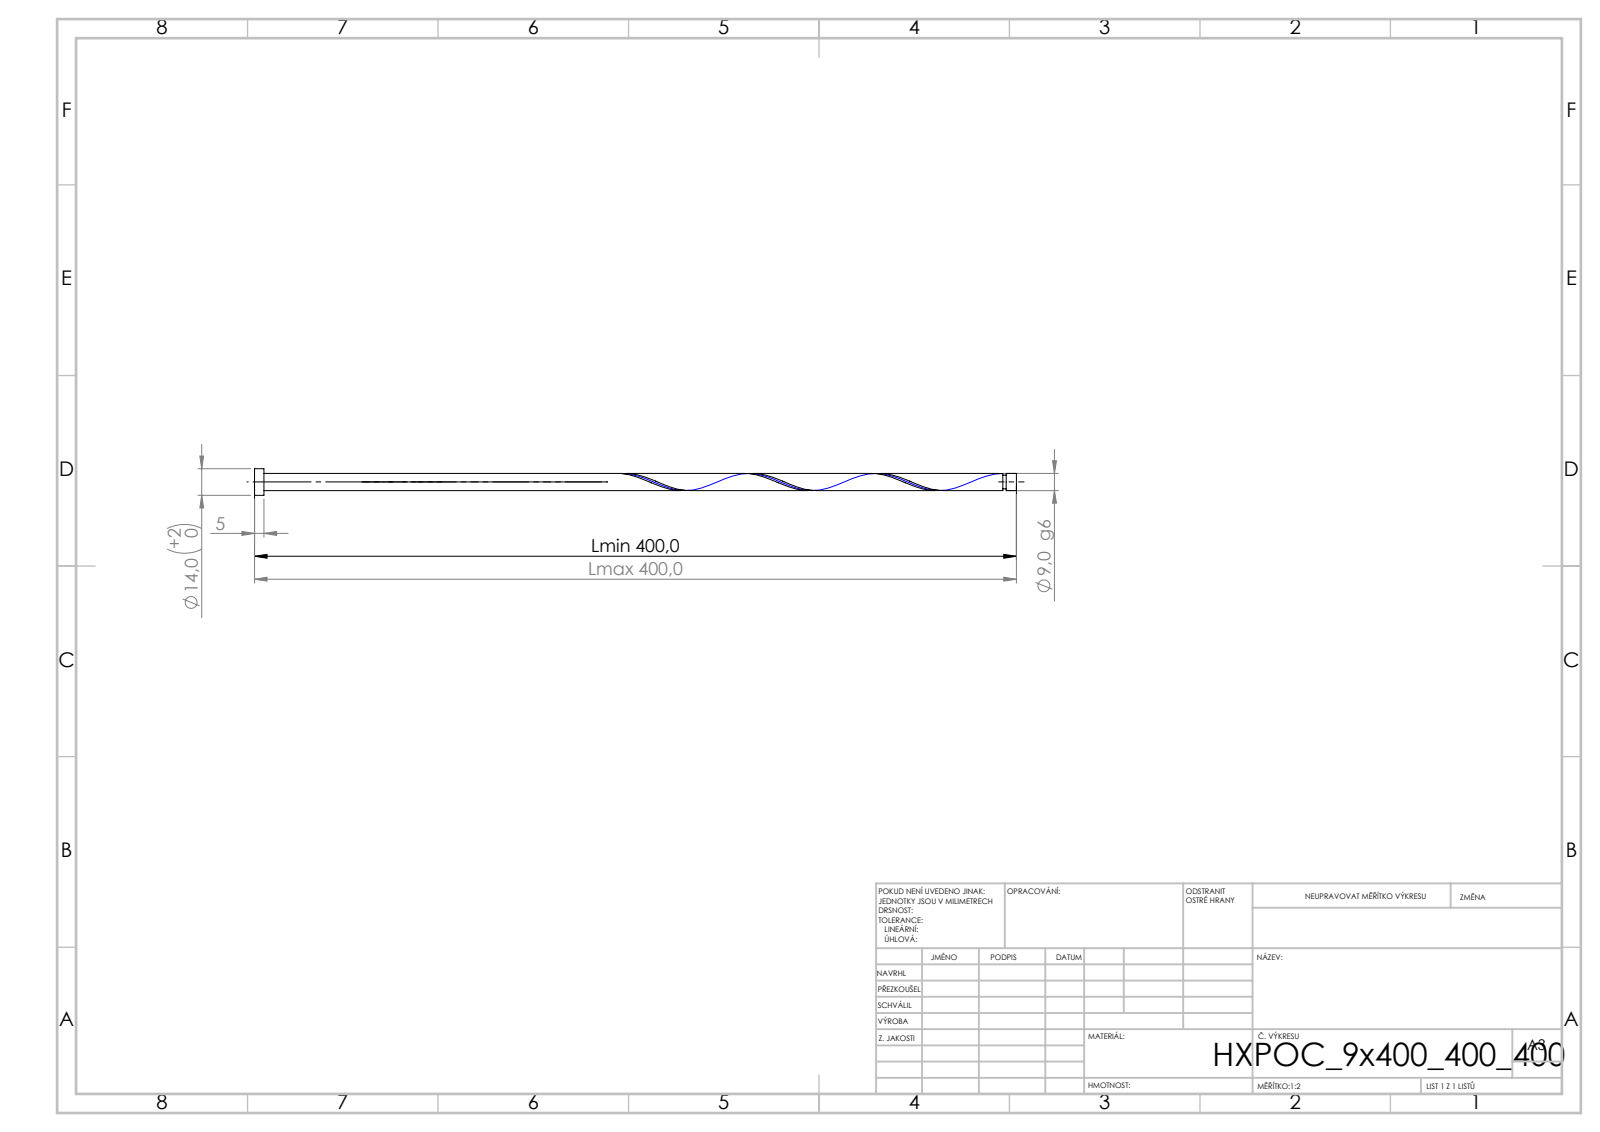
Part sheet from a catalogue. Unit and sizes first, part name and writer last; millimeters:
Units: millimetres
Overall size (bounding box): 400 × 14 × 14
Round bosses / shafts (diameter × count): ⌀14 ×1, ⌀9 ×1, ⌀7.2 ×1
Main face-to-face distances: 5, 400, 395, 394.66, 389.66, 5.34, 392.86, 387.86, 1.8, 7.14
Volume: 25 614 mm³ · Surface area: 11 922 mm²
Bodies: 1 solid, 21 faces (6 planar, 14 cylindrical, 1 other)
STEP written by: SolidWorks 2019 (CONFIG_CONTROL_DESIGN)
